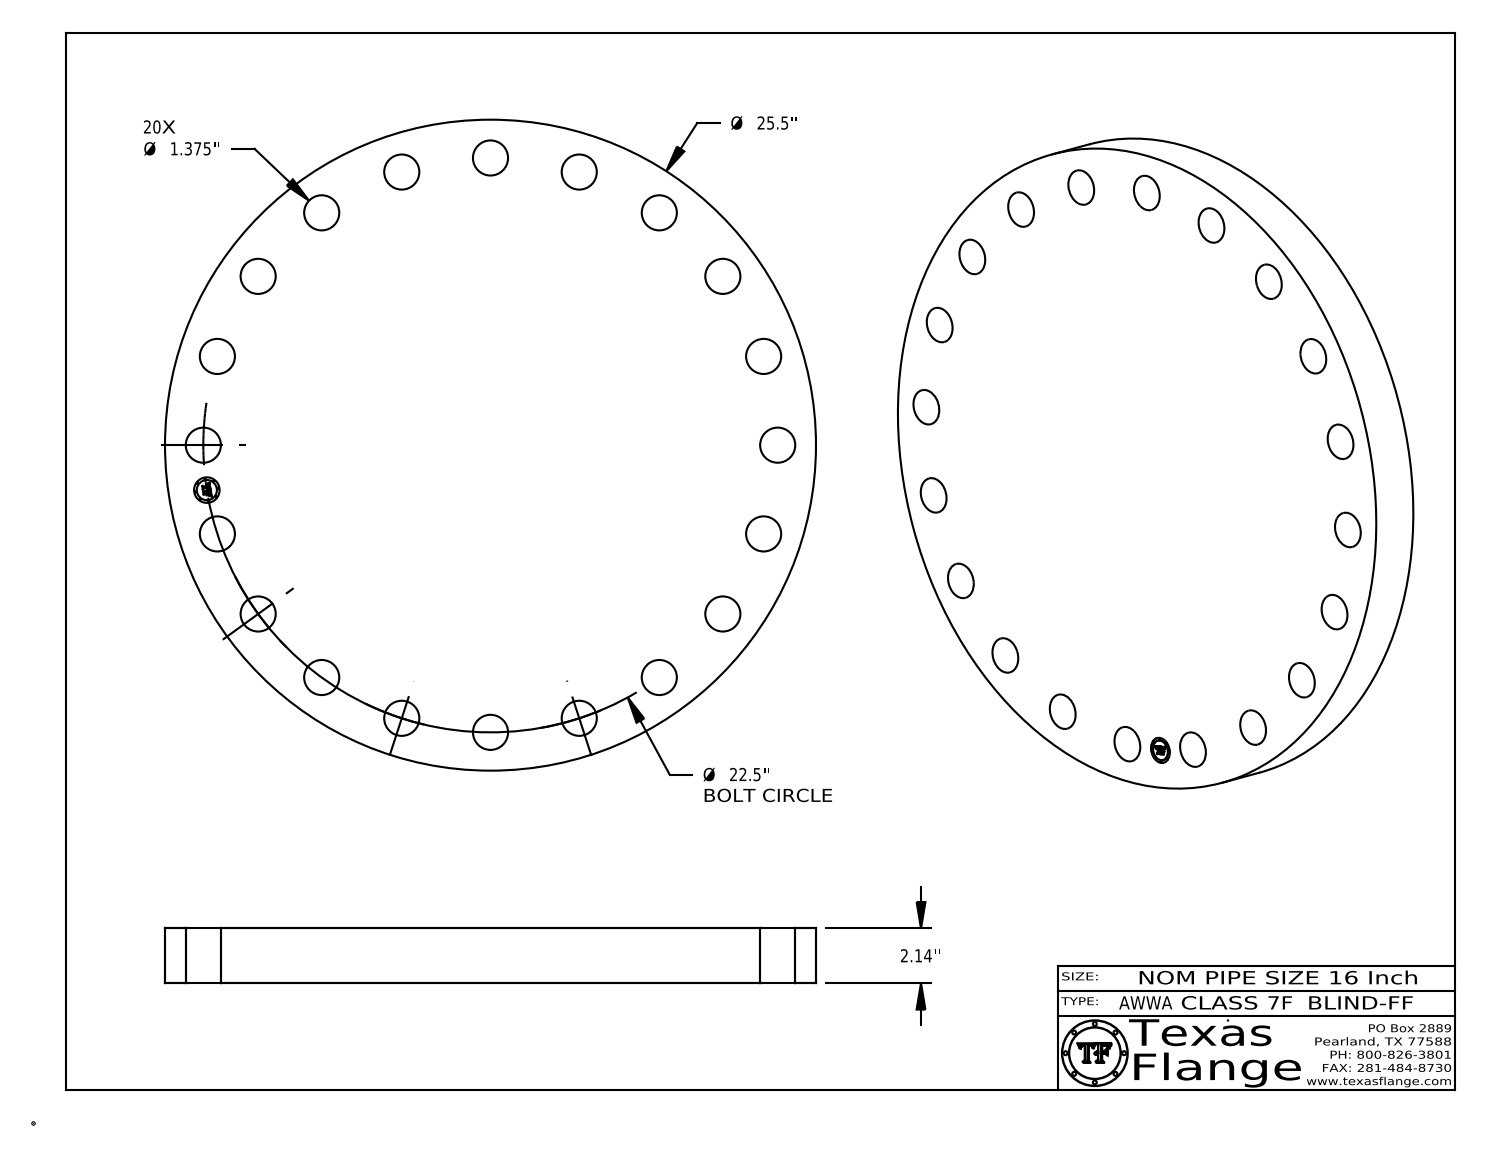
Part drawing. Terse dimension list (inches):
name: AWWA Class 7F-BLIND-FF
written by: CATIA V5 STEP AP214 (AUTOMOTIVE_DESIGN)
unit: in
bodies: 1 solid, 429 faces (367 planar, 62 cylindrical, 0 other)
size: 25.5 × 25.5 × 2.14
volume: 1 029 in³; area: 1 319 in²
holes: 20× ⌀1.375, 1× ⌀1
bosses: 8× ⌀0.061, 1× ⌀25.5, 1× ⌀0.788
face distances: 2.14, 2.125, 0.015, 0.298, 0.293, 0.054, 0.193, 0.248, 0.044, 0.15
hole spacings: 6.953, 13.225, 3.52, 18.203, 20.048, 21.399, 22.223, 10.215
